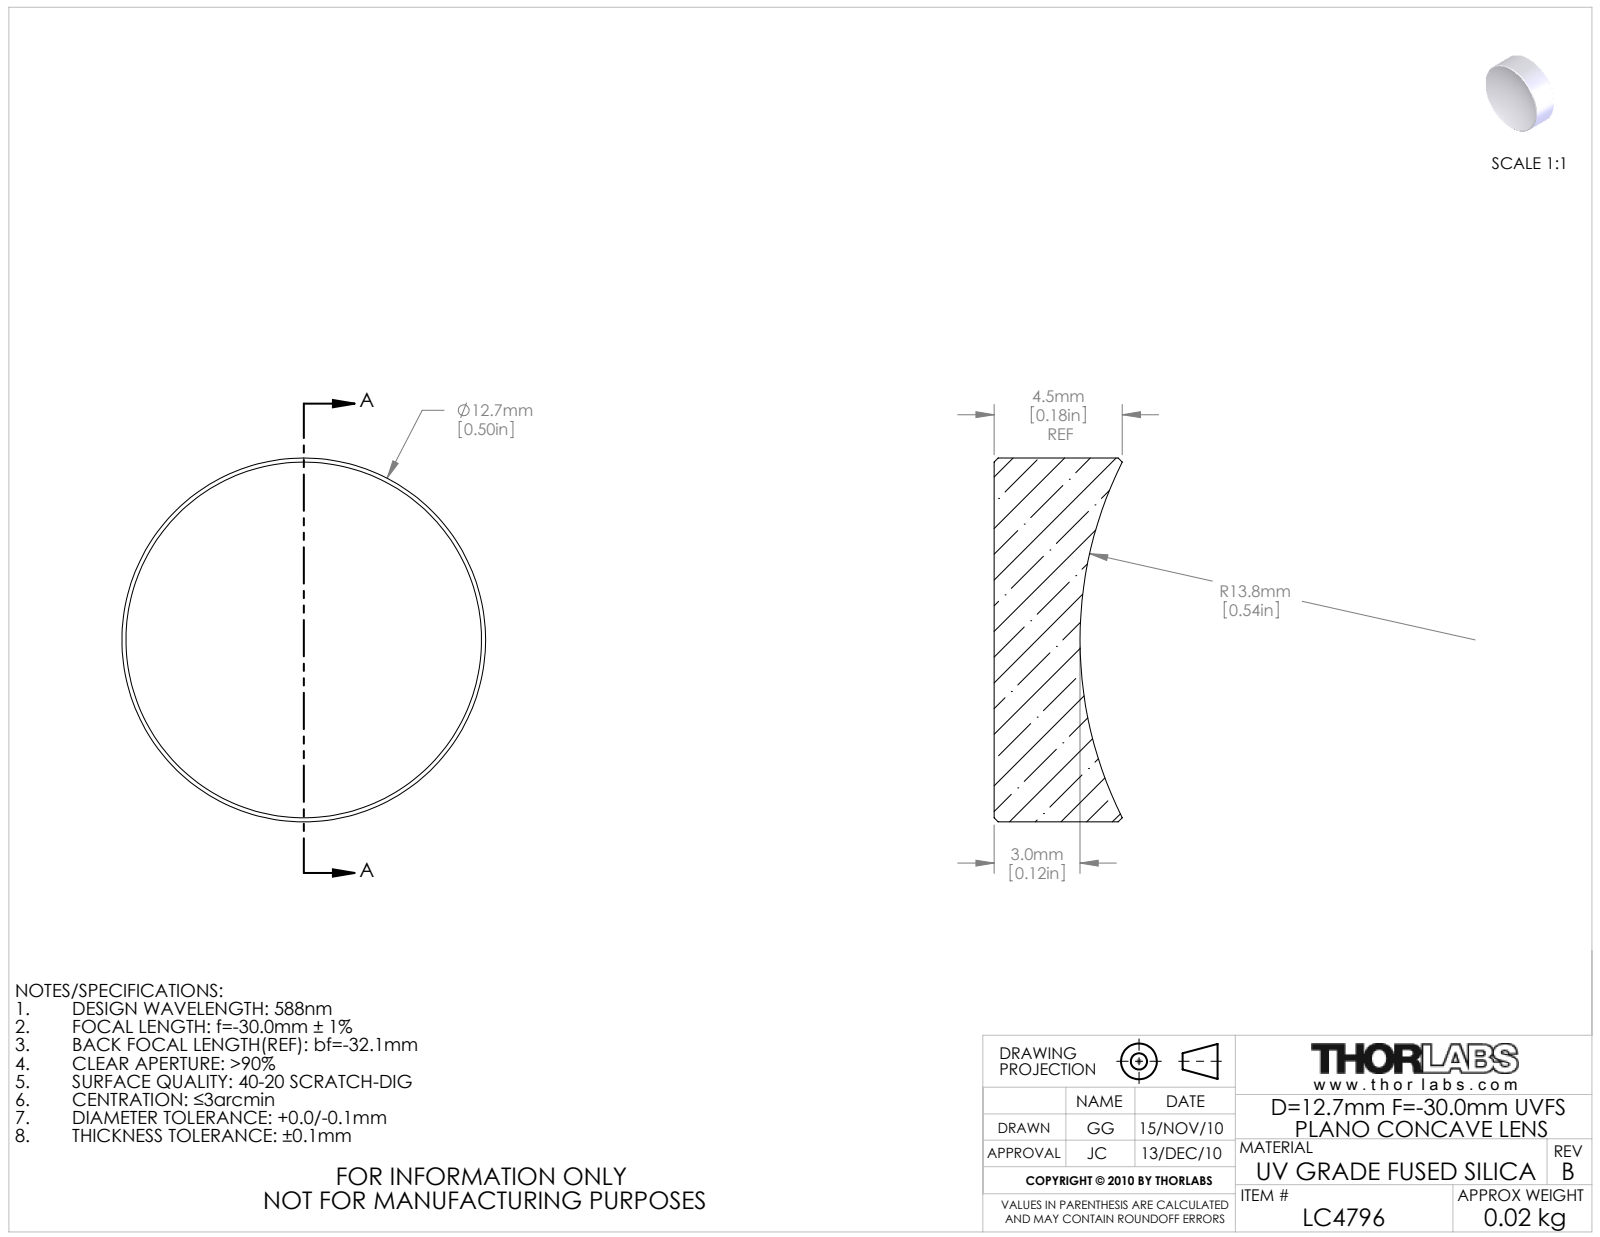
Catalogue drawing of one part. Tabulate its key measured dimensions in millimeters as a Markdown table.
| quantity | value |
| --- | --- |
| part name | 3496-E0W |
| STEP written by | SolidWorks 2009 (AUTOMOTIVE_DESIGN) |
| units | millimeters |
| bodies | 1 solid, 9 faces (1 planar, 2 cylindrical, 6 other) |
| overall size | 12.7 × 12.7 × 4.47 |
| volume | 475 mm³ |
| surface area | 432 mm² |
| round bosses / shafts (diameter × count) | 12.7 × 1 |
